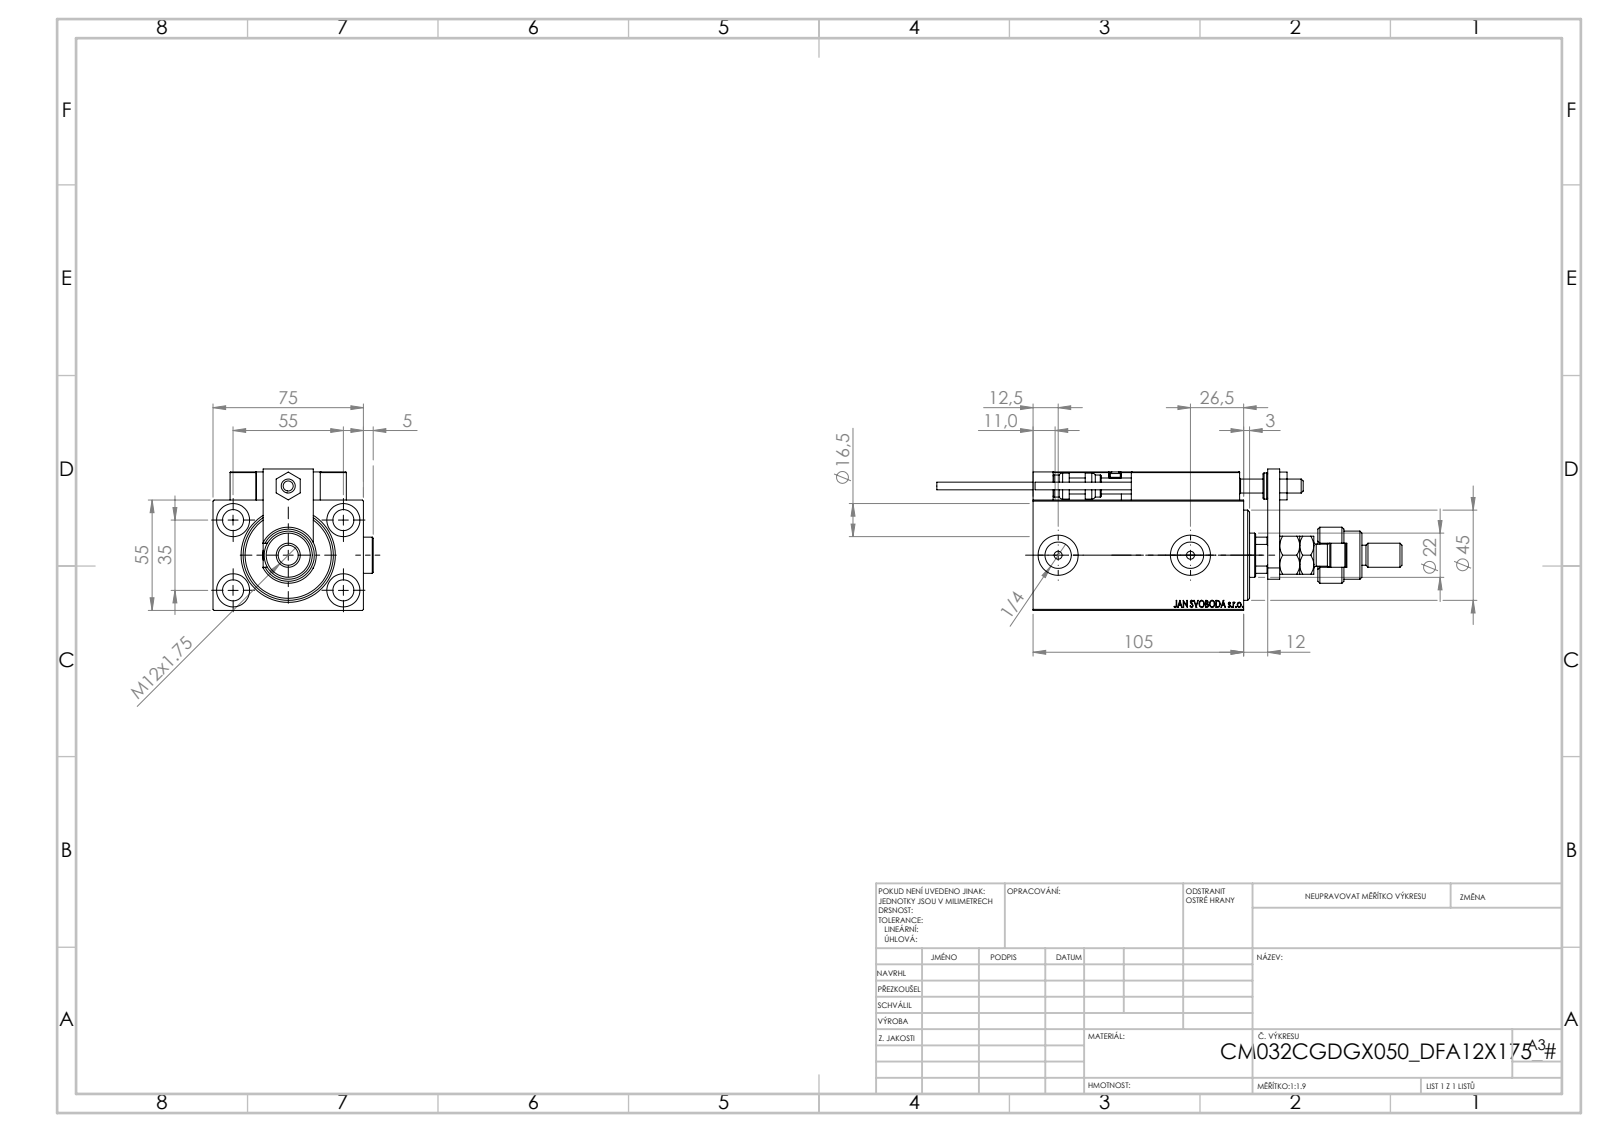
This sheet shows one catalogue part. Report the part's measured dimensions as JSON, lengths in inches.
{"part_name": "SWITCH DIM B,W; KONCOVKA; SWITCH X; Zatka_OIL_PORT (+7 more)", "step_written_by": "SolidWorks 2019 (CONFIG_CONTROL_DESIGN)", "units": "inches", "bodies": {"solids": 27, "faces": 1421, "planar": 622, "cylindrical": 217, "other": 582}, "overall_size": [9.134, 3.146, 2.776], "volume_in3": 26.34, "surface_area_in2": 173.8, "round_holes": [[0.157, 6], [0.315, 5], [0.413, 5], [0.65, 5], [0.126, 4], [0.197, 2], [0.518, 2], [0.787, 2], [0.276, 1], [0.866, 1], [1.004, 1], [1.26, 1]], "round_bosses_or_shafts": [[0.709, 3], [0.433, 2], [0.197, 2], [0.15, 2], [1.102, 1], [0.945, 1], [0.512, 1], [0.472, 1]], "partial_cylinders_radius": [[0.012, 30], [0.118, 2], [0.384, 1], [0.413, 1]], "face_to_face_distances": [2.165, 2.953, 0.551, 0.472, 0.394, 0.197, 0.709, 0.236, 0.984, 2.717], "hole_center_spacings": [1.283, 0.448, 0.787, 1.165, 1.169, 1.273, 1.378, 1.42]}
